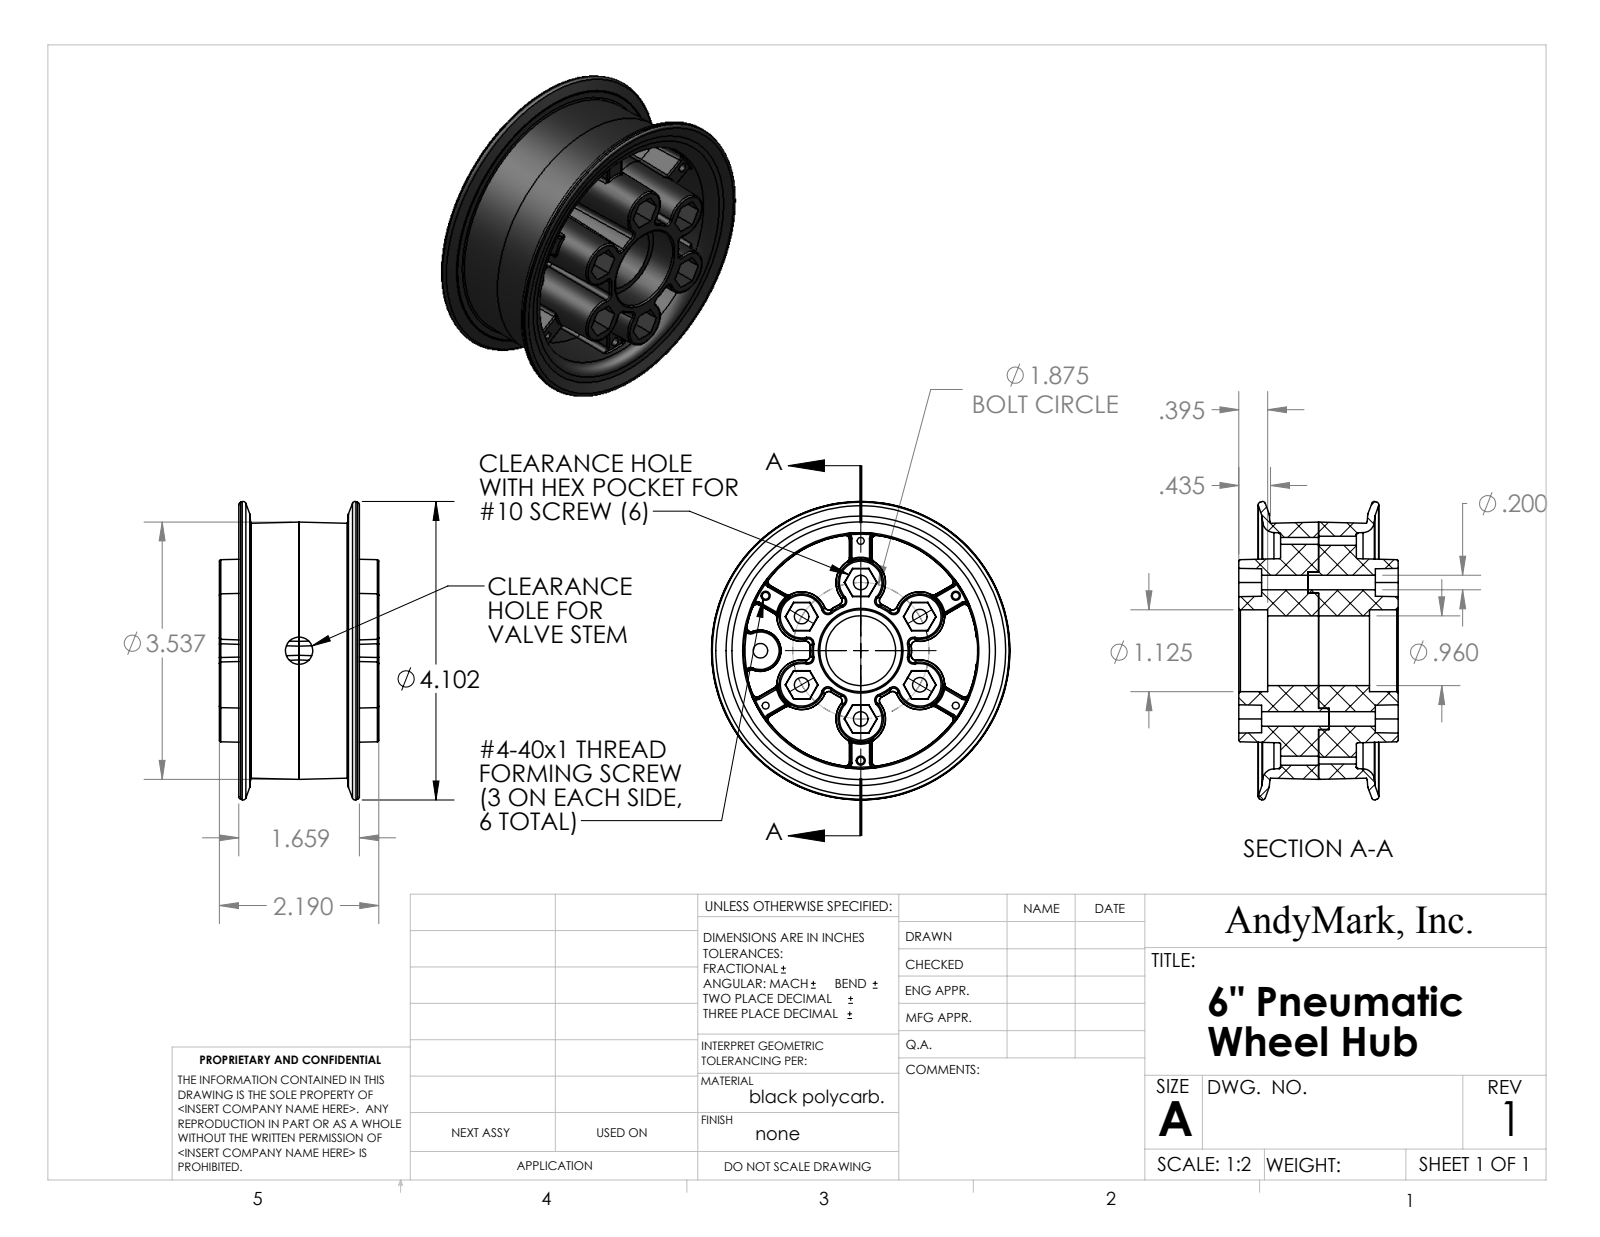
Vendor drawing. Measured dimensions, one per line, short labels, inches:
name: 6 Hub; am-2469 6in pneumatic wheel hub assembly
written by: SolidWorks 2014 (AUTOMOTIVE_DESIGN)
unit: in
bodies: 2 solids, 618 faces (140 planar, 112 cylindrical, 366 other)
size: 4.102 × 4.102 × 2.19
volume: 8.509 in³; area: 111.2 in²
holes: 7× ⌀0.2, 6× ⌀0.125, 4× ⌀0.095, 4× ⌀0.295, 2× ⌀0.095, 2× ⌀0.295, 1× ⌀0.375, 1× ⌀0.96, 1× ⌀1.125
bosses: 6× ⌀0.29
rounds: 14× R0.02
face distances: 1.406, 0.354, 1.095, 2.19, 1.095, 0.313, 1.878, 0.353, 0.307, 0.937
hole spacings: 2.139, 1.51, 0.937, 0.572, 1.32, 1.32, 2.448, 2.615
